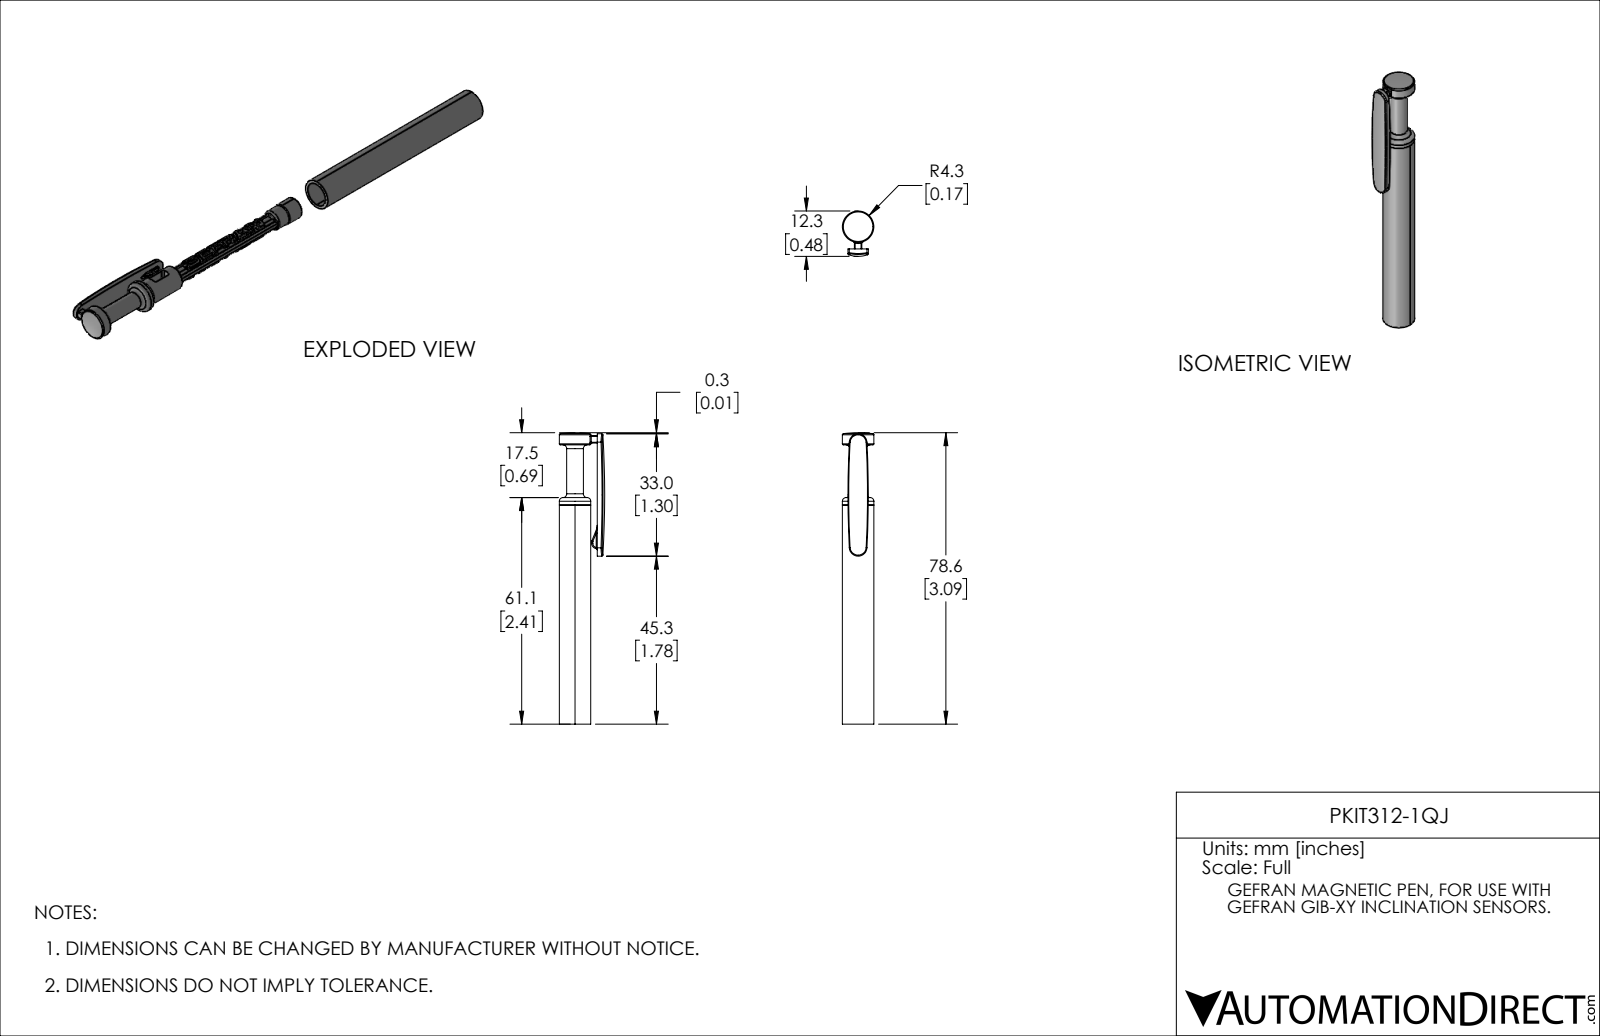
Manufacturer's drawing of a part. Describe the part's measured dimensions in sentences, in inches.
The part is named "PKIT312-1QJ". Its 3-D file was written by "SolidWorks 2021 (AUTOMOTIVE_DESIGN)". It is 2 solids with 1313 faces: 168 planar, 325 cylindrical and 820 other. Overall it measures 3.094 by 0.482 by 0.335 inches. Its volume is 0.206 cubic inches and its surface area 7.835 square inches. Round bosses or shafts: 1 of diameter 0.335, 1 of diameter 0.236, 1 of diameter 0.22, 1 of diameter 0.177. Partial cylindrical surfaces (rounded edges, fillets, slot ends): 101 of radius 0.008, 12 of radius 0.007, 12 of radius 0.012, 11 of radius 0.02, 6 of radius 0.016, 6 of radius 0.035, 4 of radius 0.004, 4 of radius 0.009. The main face-to-face distances are 0.335, 0.138, 2.327, 0.197, 0.049, 0.148, 2.283, 0.043, 0.02, 2.28.
